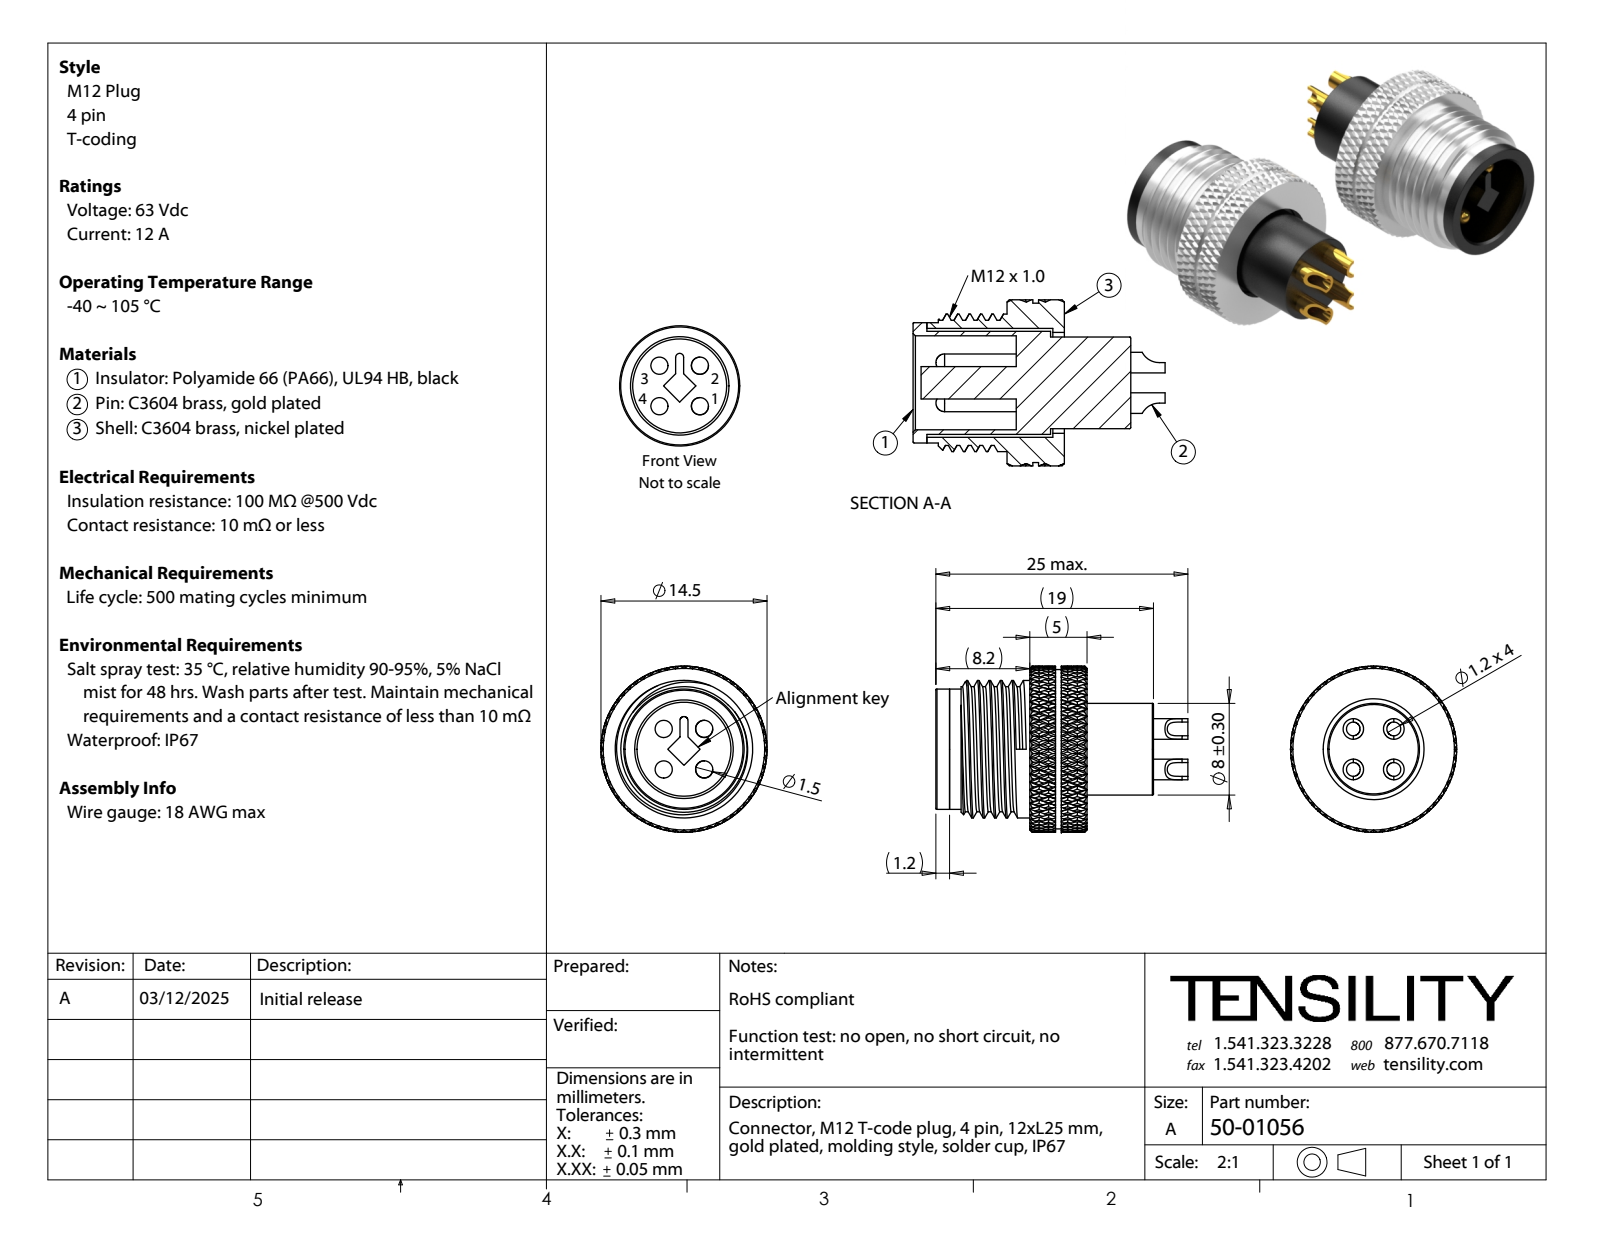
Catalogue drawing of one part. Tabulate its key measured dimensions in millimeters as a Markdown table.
| quantity | value |
| --- | --- |
| part name | 50-01056-02_step; 50-01056-03; 50-01056-03L; 50-01056-01 (+1 more) |
| STEP written by | SolidWorks 2021 (CONFIG_CONTROL_DESIGN) |
| units | millimeters |
| bodies | 6 solids, 216 faces (52 planar, 100 cylindrical, 64 other) |
| overall size | 22 × 14.5 × 14.5 |
| volume | 1 448 mm³ |
| surface area | 2 860 mm² |
| round holes (diameter × count) | 1.2 × 4, 1.5 × 4, 8.2 × 1, 8.8 × 1, 9.5 × 1 |
| round bosses / shafts (diameter × count) | 1.8 × 4, 14.5 × 1, 13.9 × 1, 12 × 1, 10.5 × 1, 9 × 1, 8 × 1 |
| partial cylindrical surfaces (radius × count) | 1.7 × 2, 0.35 × 1 |
| main face-to-face distances | 12, 10, 7, 10.8, 5, 0.8, 7.8, 4.2, 5.8, 1.2 |
| hole center spacings | 2.5, 3.54, 5.01 |
